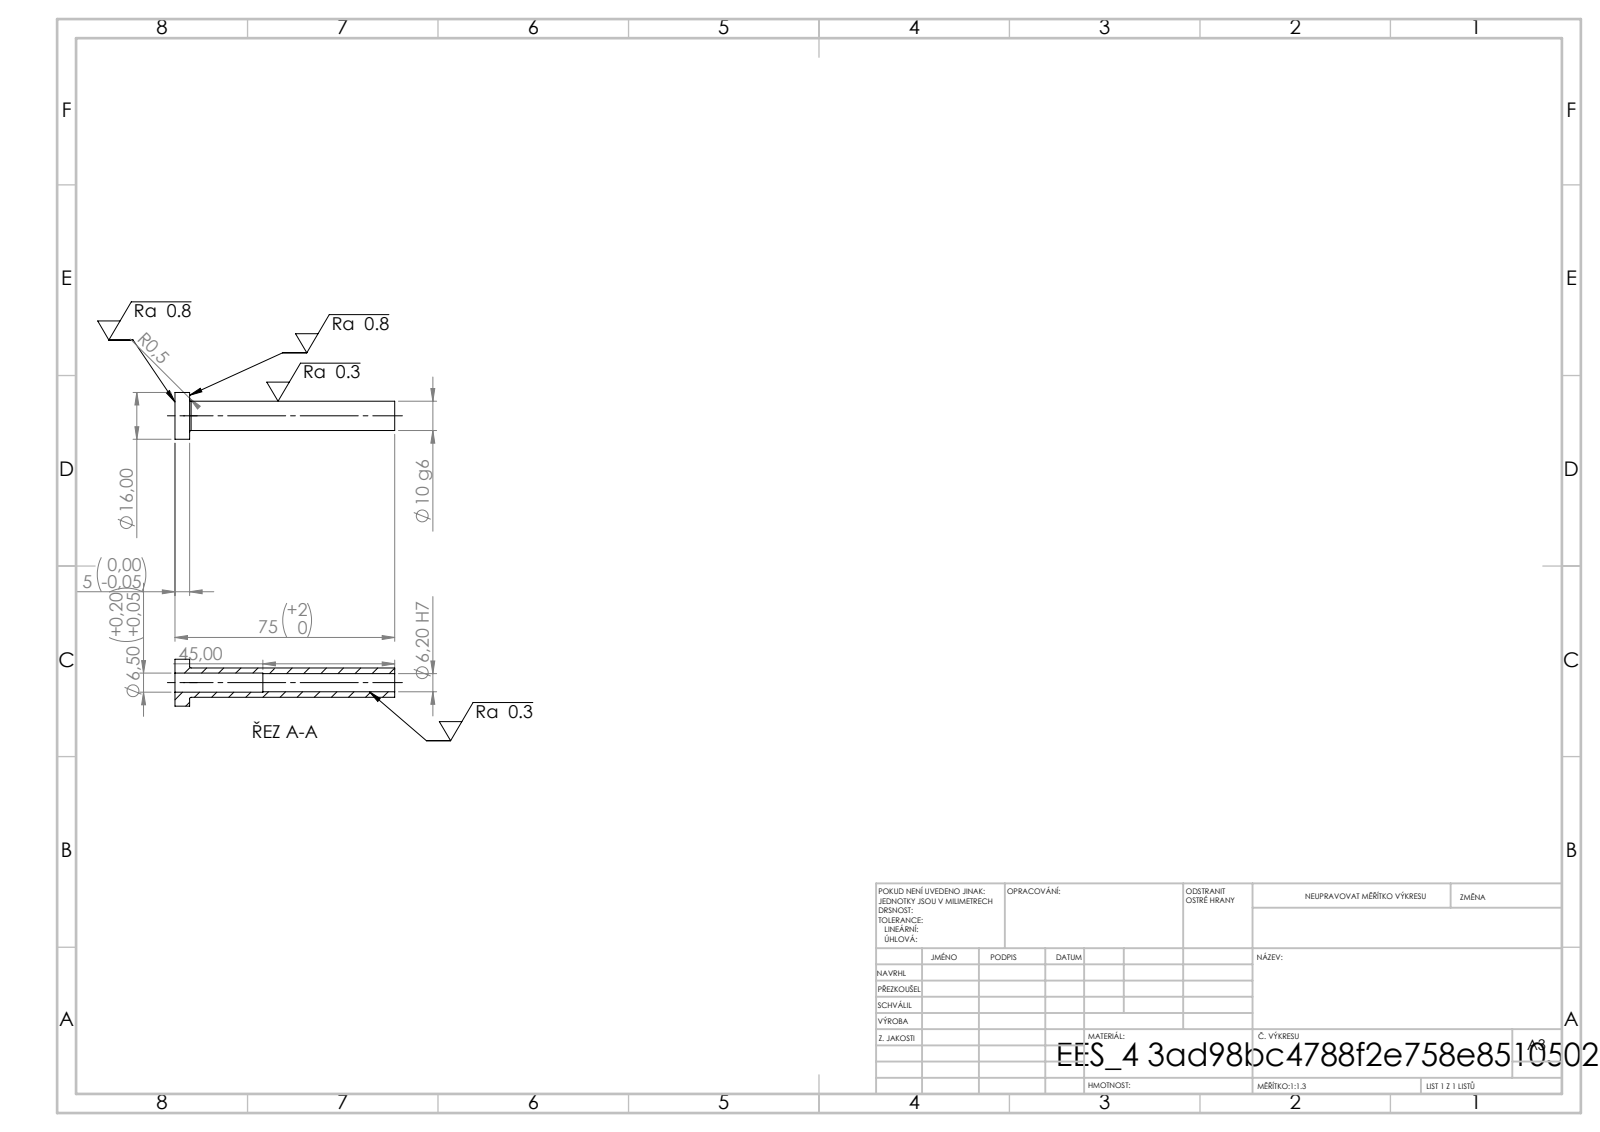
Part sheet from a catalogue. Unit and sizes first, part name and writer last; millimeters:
Units: millimetres
Overall size (bounding box): 75 × 16 × 16
Round holes (diameter × count): ⌀6.2 ×1, ⌀6.5 ×1
Round bosses / shafts (diameter × count): ⌀16 ×1, ⌀10 ×1
Main face-to-face distances: 5, 75, 70, 30, 25, 45
Volume: 4 151 mm³ · Surface area: 4 275 mm²
Bodies: 1 solid, 14 faces (4 planar, 8 cylindrical, 2 other)
STEP written by: SolidWorks 2019 (CONFIG_CONTROL_DESIGN)
